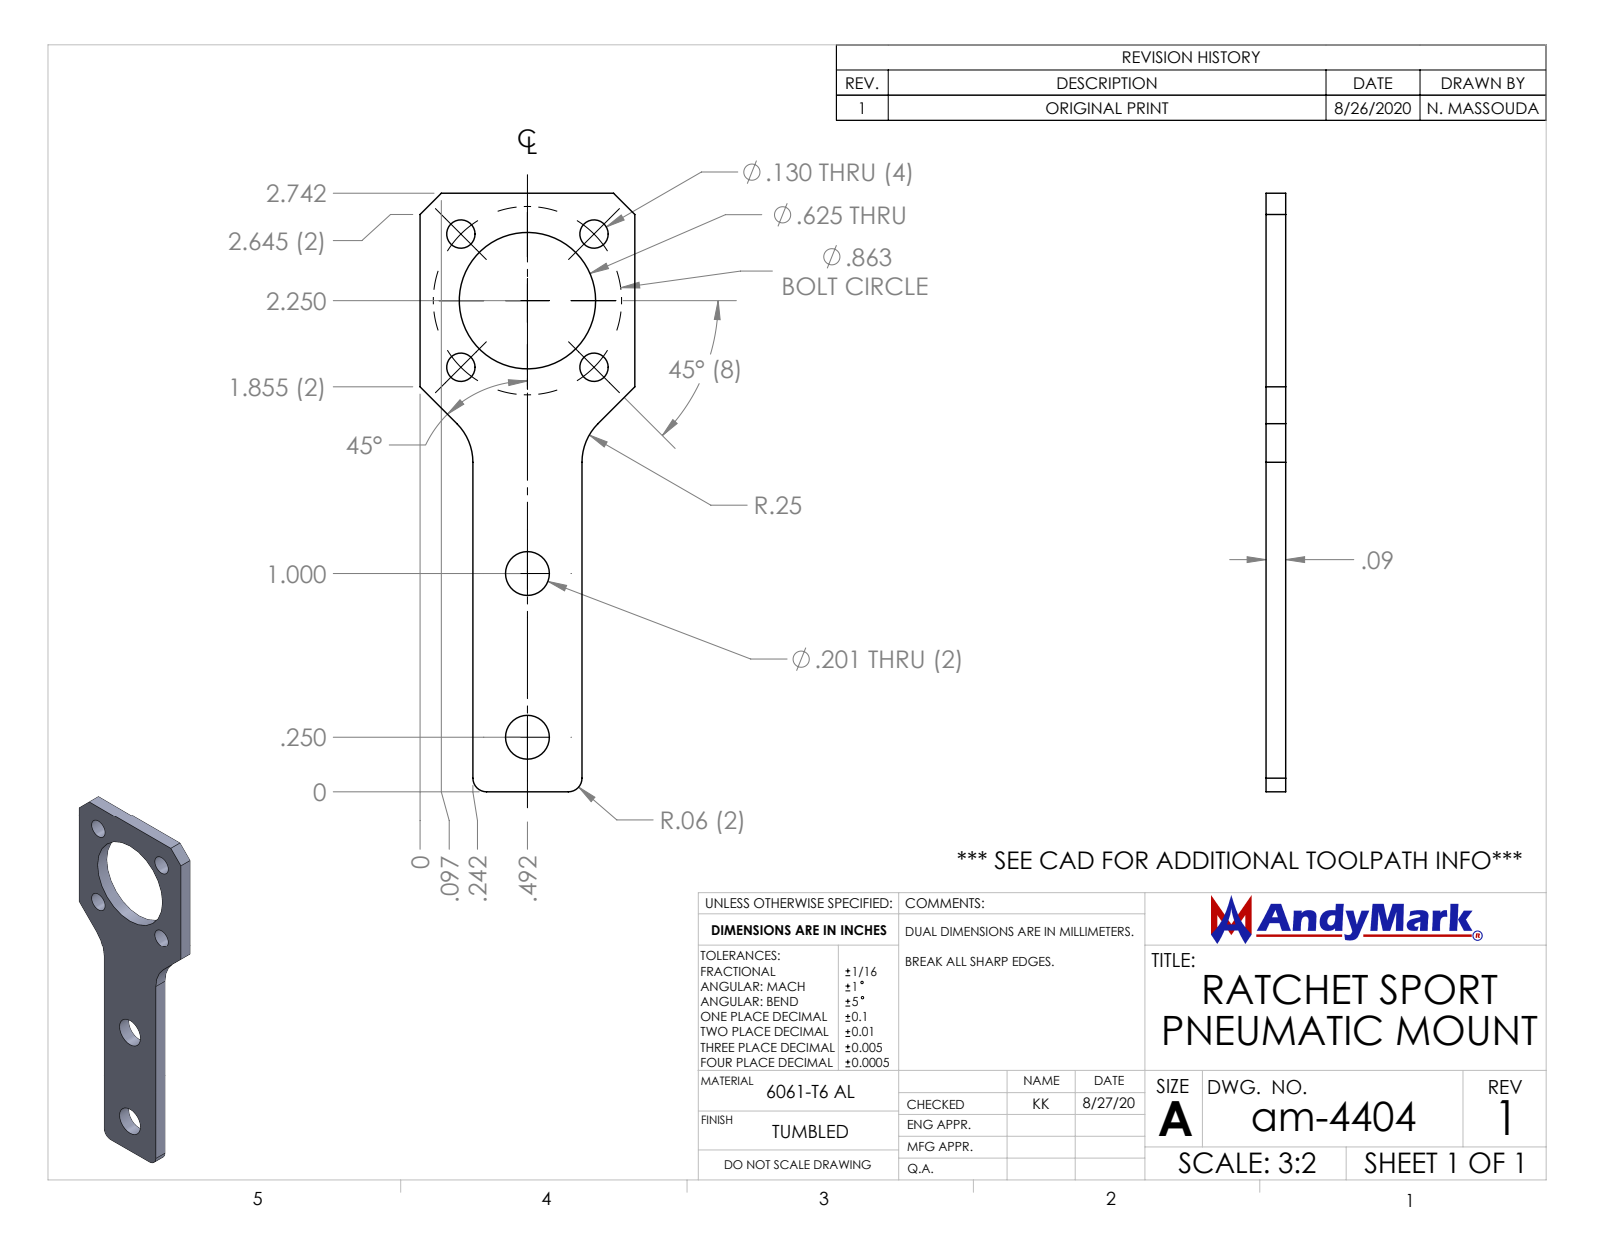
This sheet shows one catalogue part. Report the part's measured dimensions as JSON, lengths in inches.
{"part_name": "am-4404 Ratchet Sport Pneumatic Mount", "step_written_by": "SolidWorks 2019 (CONFIG_CONTROL_DESIGN)", "units": "inches", "bodies": {"solids": 1, "faces": 30, "planar": 12, "cylindrical": 18, "other": 0}, "overall_size": [2.742, 0.984, 0.09], "volume_in3": 0.128, "surface_area_in2": 3.92, "round_holes": [[0.13, 4], [0.201, 2], [0.625, 1]], "partial_cylinders_radius": [[0.25, 2], [0.062, 1], [0.063, 1]], "face_to_face_distances": [0.09, 0.242, 0.742, 0.5, 0.984, 2.742, 1.254], "hole_center_spacings": [0.431, 0.61, 0.863, 0.993, 1.585, 1.722, 2.325, 0.75]}
